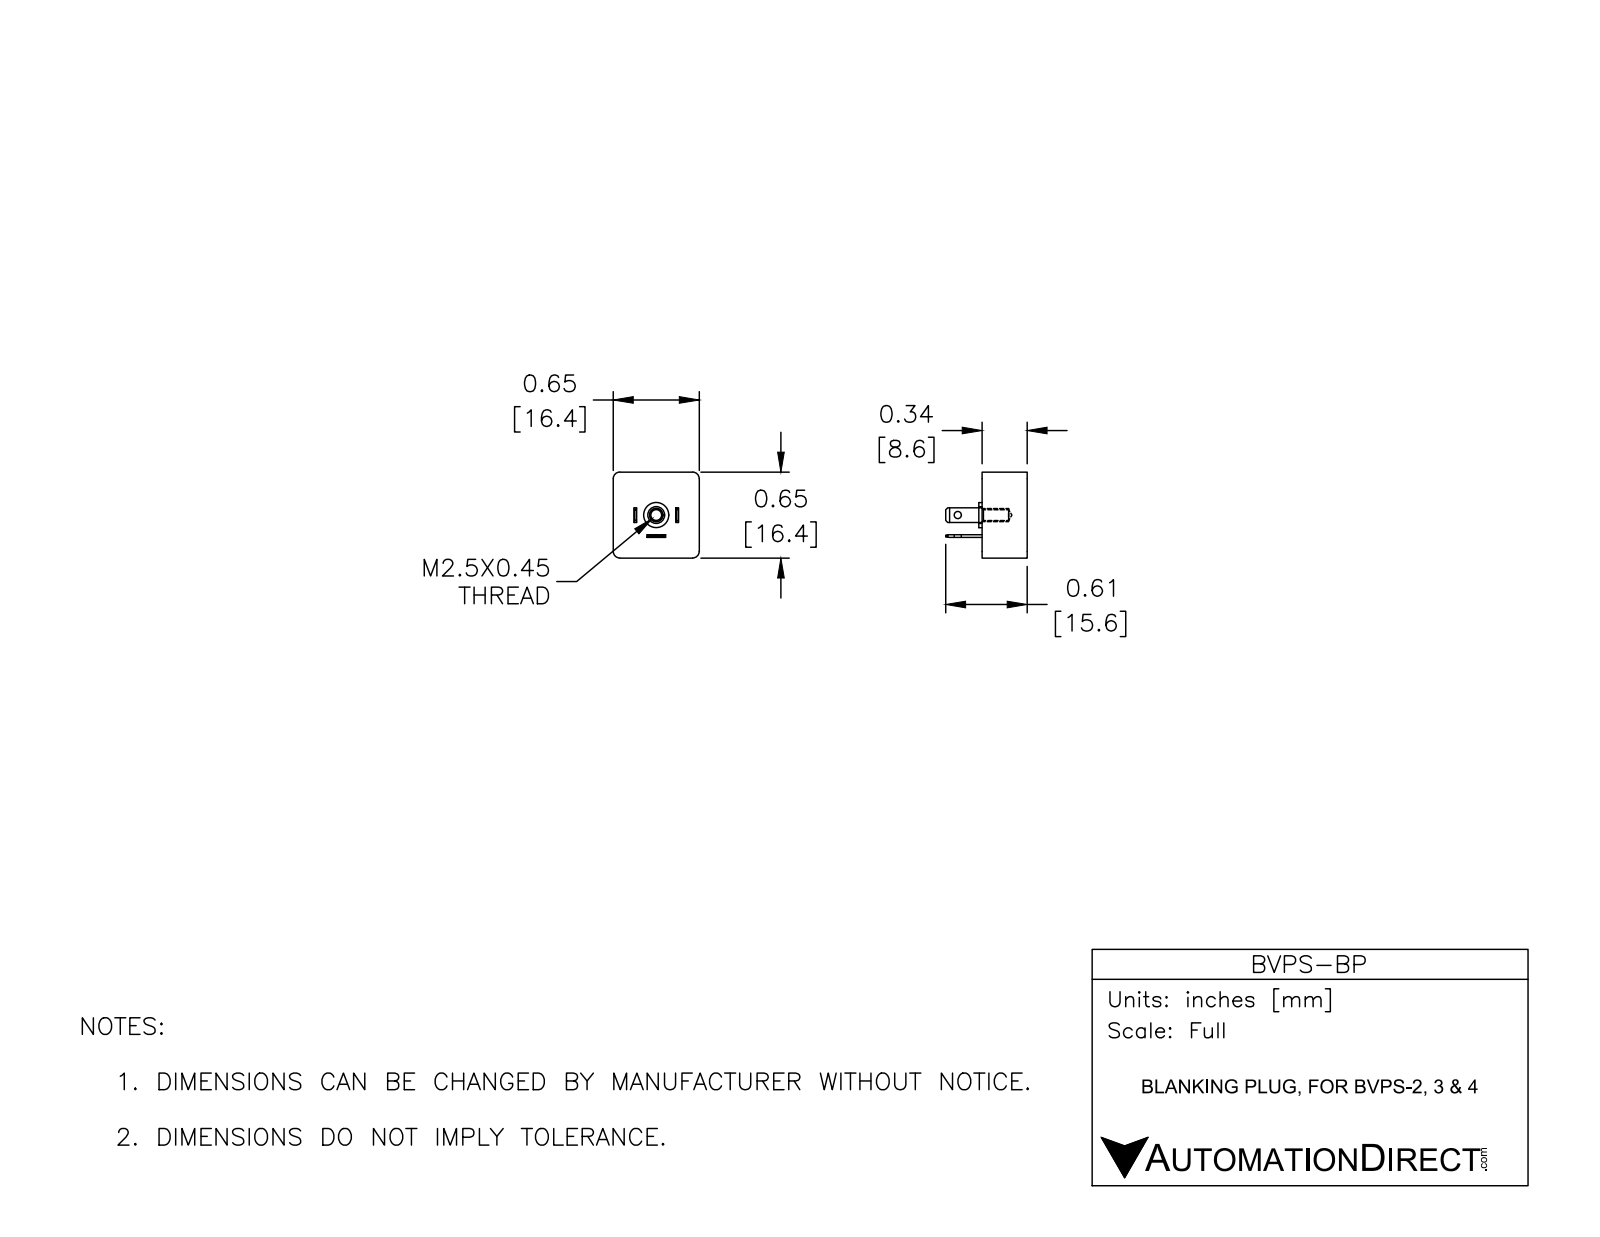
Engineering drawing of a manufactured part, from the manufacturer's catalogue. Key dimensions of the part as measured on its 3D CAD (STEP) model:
Part name (STEP PRODUCT): BVPS-BP
STEP written by: SolidWorks 2016 (AUTOMOTIVE_DESIGN)
Units: inches
Bodies: 1 solid, 55 faces (35 planar, 16 cylindrical, 4 other)
Overall size (bounding box): 0.647 × 0.647 × 0.613
Volume: 0.142 in³ · Surface area: 1.979 in²
Round holes (diameter × count): ⌀0.053 ×2, ⌀0.081 ×1, ⌀0.126 ×1
Round bosses / shafts (diameter × count): ⌀0.189 ×1
Partial cylindrical surfaces — rounded edges, fillets, slot ends (radius × count): R0.05 ×4
Main face-to-face distances: 0.339, 0.647, 0.156, 0.176, 0.471, 0.491, 0.02, 0.315, 0.335, 0.295
